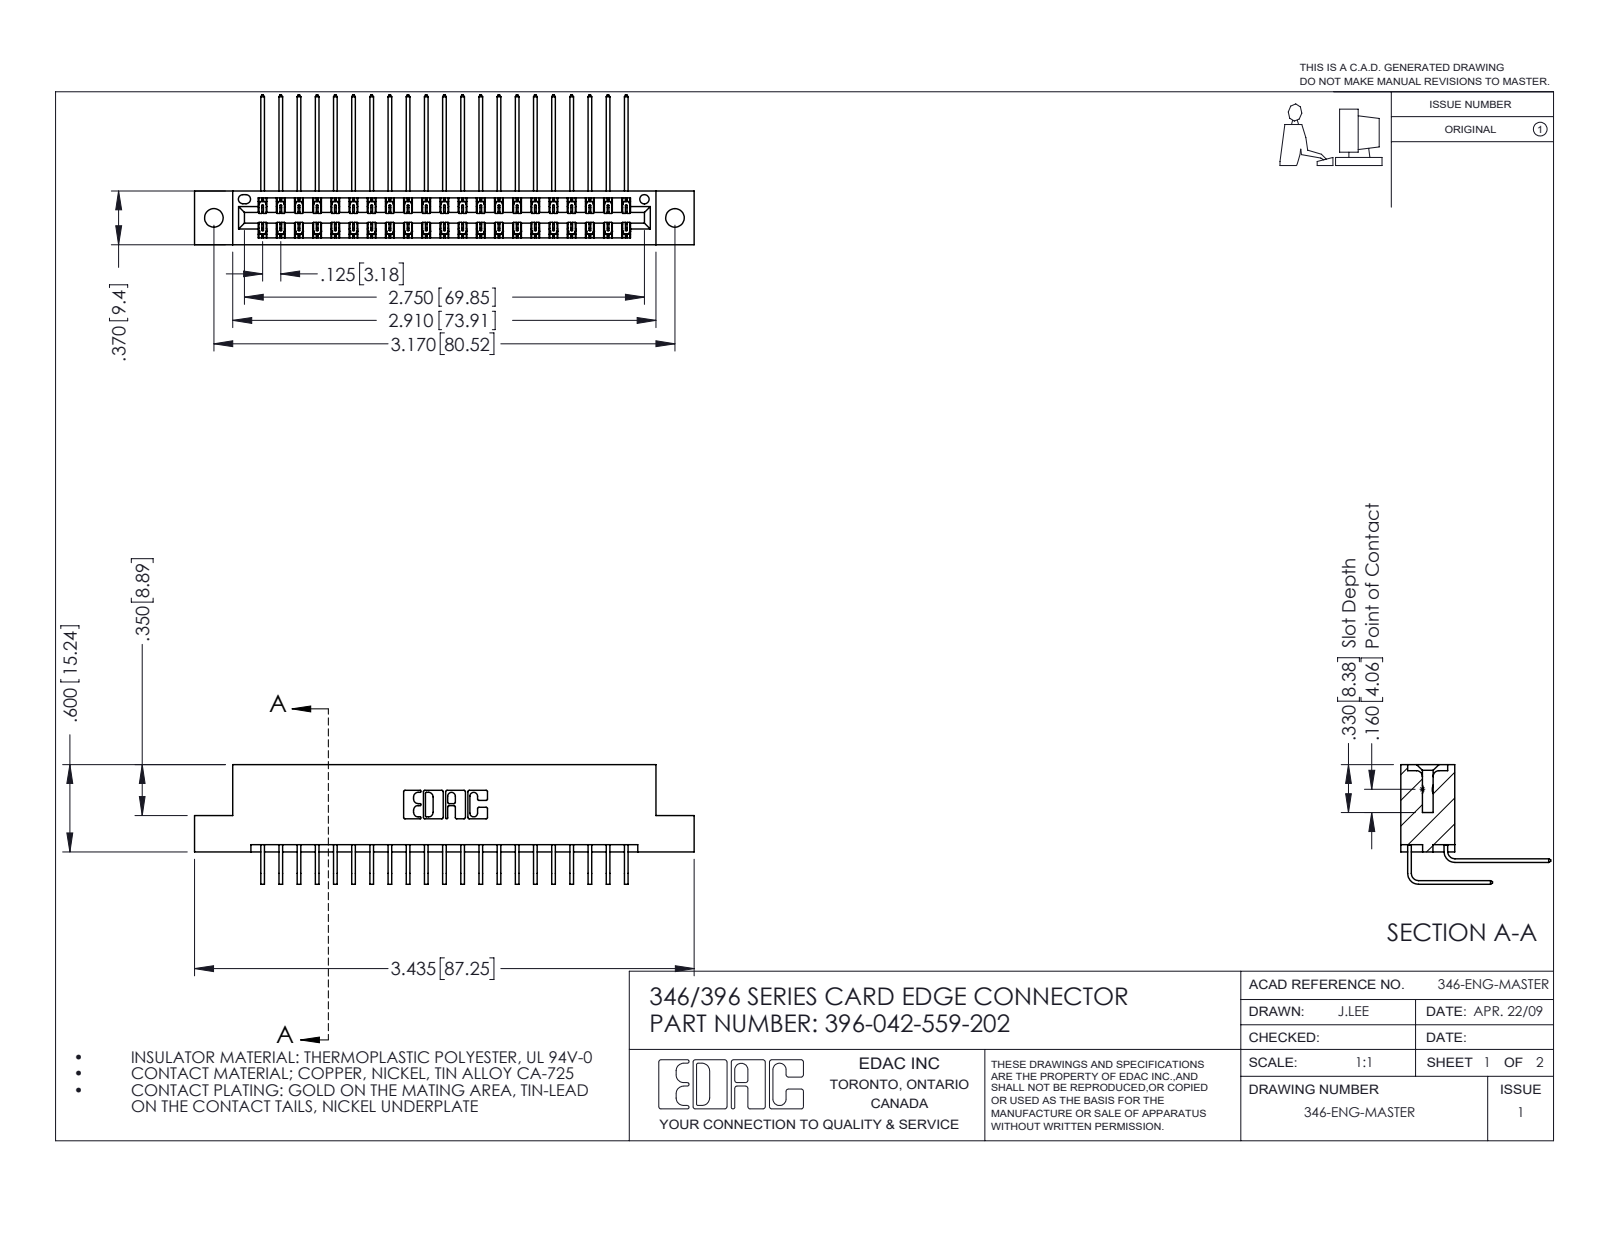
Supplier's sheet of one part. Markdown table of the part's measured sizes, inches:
| quantity | value |
| --- | --- |
| part name | 345-292-001_558 559 Tail - 1; 345-292-001_559 Tail - 2; 346 Part_Flush Mounting Lugs - 0.128 Dia; 396-042-559-202 |
| STEP written by | SolidWorks 2016 (CONFIG_CONTROL_DESIGN) |
| units | inches |
| bodies | 43 solids, 2390 faces (1630 planar, 760 cylindrical, 0 other) |
| overall size | 3.435 × 1.03 × 0.823 |
| volume | 0.522 in³ |
| surface area | 19.09 in² |
| round holes (diameter × count) | 0.128 × 2, 0.064 × 1 |
| partial cylindrical surfaces (radius × count) | 0.006 × 63, 0.01 × 22, 0.007 × 6, 0.031 × 6, 0.026 × 3, 0.014 × 2, 0.022 × 2, 0.024 × 2 |
| main face-to-face distances | 0.048, 0.322, 0.25, 0.025, 0.37, 0.072, 0.298, 0.275, 0.148, 0.222 |
| hole center spacings | 0.246, 2.963, 3.17 |
